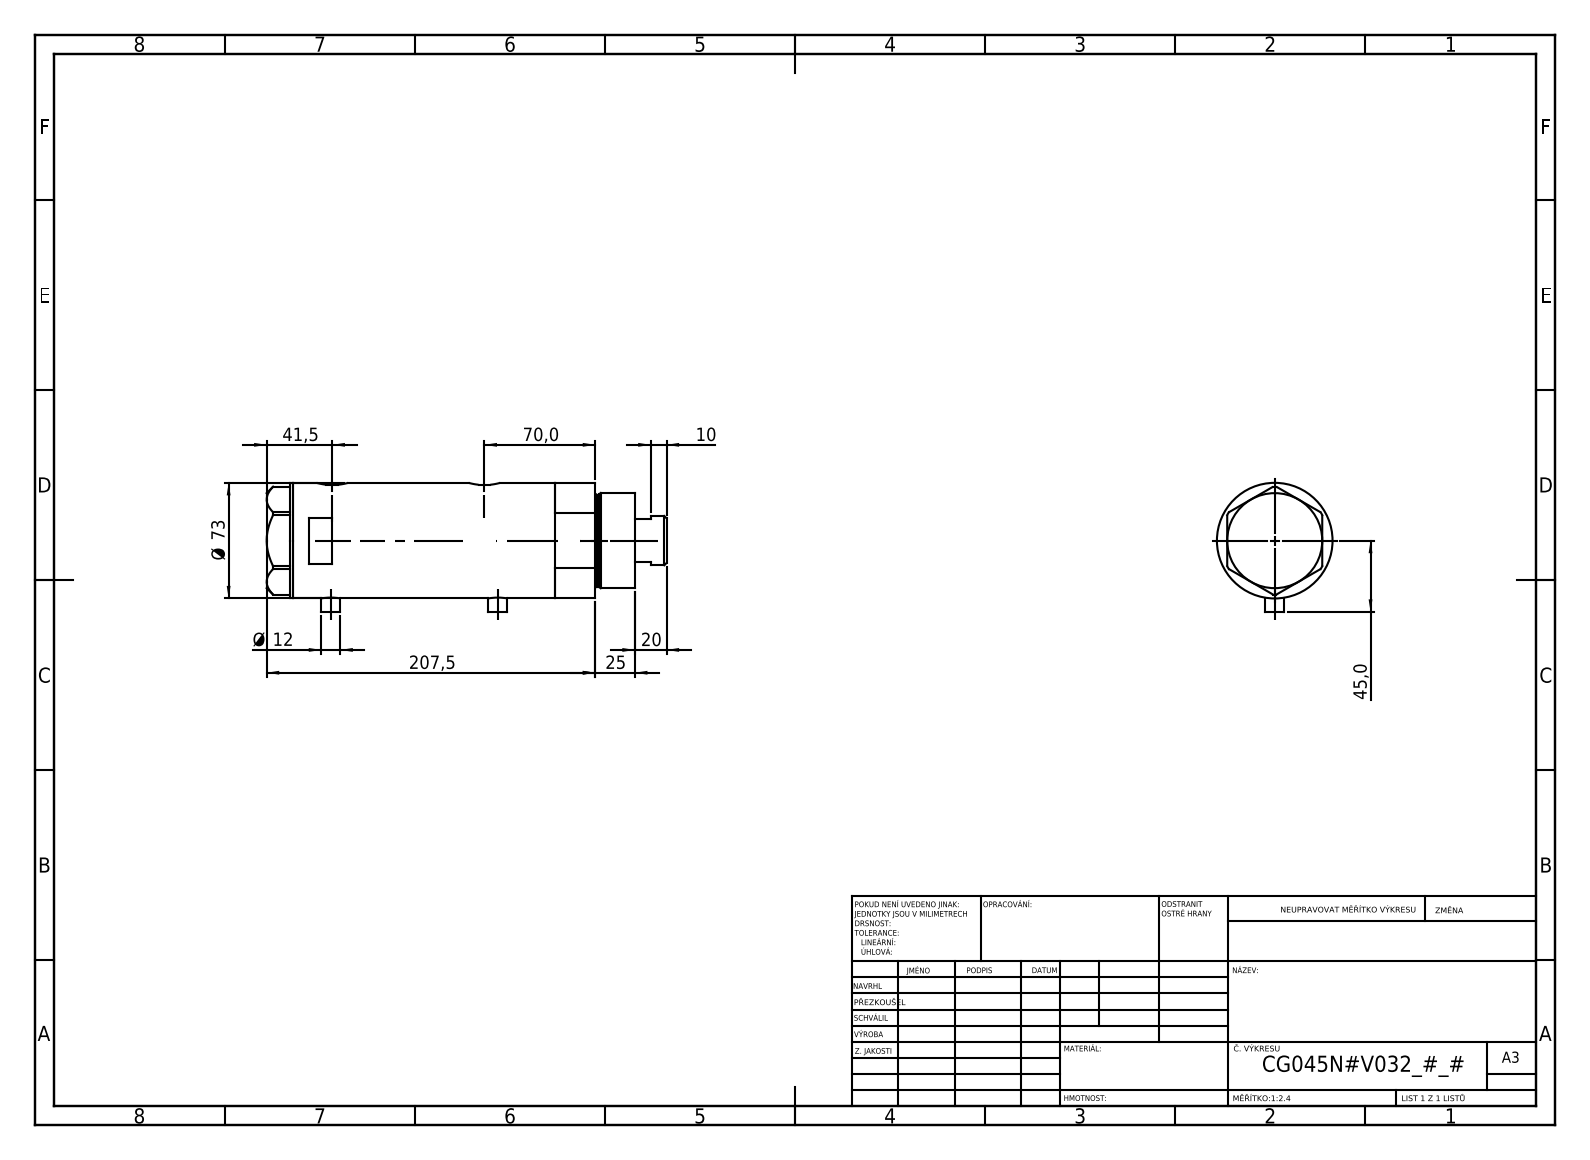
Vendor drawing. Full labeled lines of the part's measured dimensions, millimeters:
Part name (STEP PRODUCT): V270CG_FRONT; V270CG_BACK; V270CG_MIDDLE; V270CG_VC
STEP written by: SolidWorks 2019 (CONFIG_CONTROL_DESIGN)
Units: millimetres
Bodies: 4 solids, 120 faces (49 planar, 51 cylindrical, 20 other)
Overall size (bounding box): 252.5 × 81.5 × 73
Volume: 897 937 mm³ · Surface area: 149 563 mm²
Round holes (diameter × count): ⌀12.5 ×2, ⌀13.16 ×2, ⌀10.5 ×1, ⌀32 ×1, ⌀33.5 ×1, ⌀45 ×1, ⌀48 ×1, ⌀64 ×1
Round bosses / shafts (diameter × count): ⌀12 ×2, ⌀73 ×1, ⌀60 ×1, ⌀58 ×1, ⌀31 ×1
Partial cylindrical surfaces — rounded edges, fillets, slot ends (radius × count): R10 ×2
Main face-to-face distances: 95, 121, 26, 16.5, 42.5, 137.5, 60, 2, 216, 232.5
Hole centre spacings: 1, 8.5, 96, 97, 104.5, 105.5
